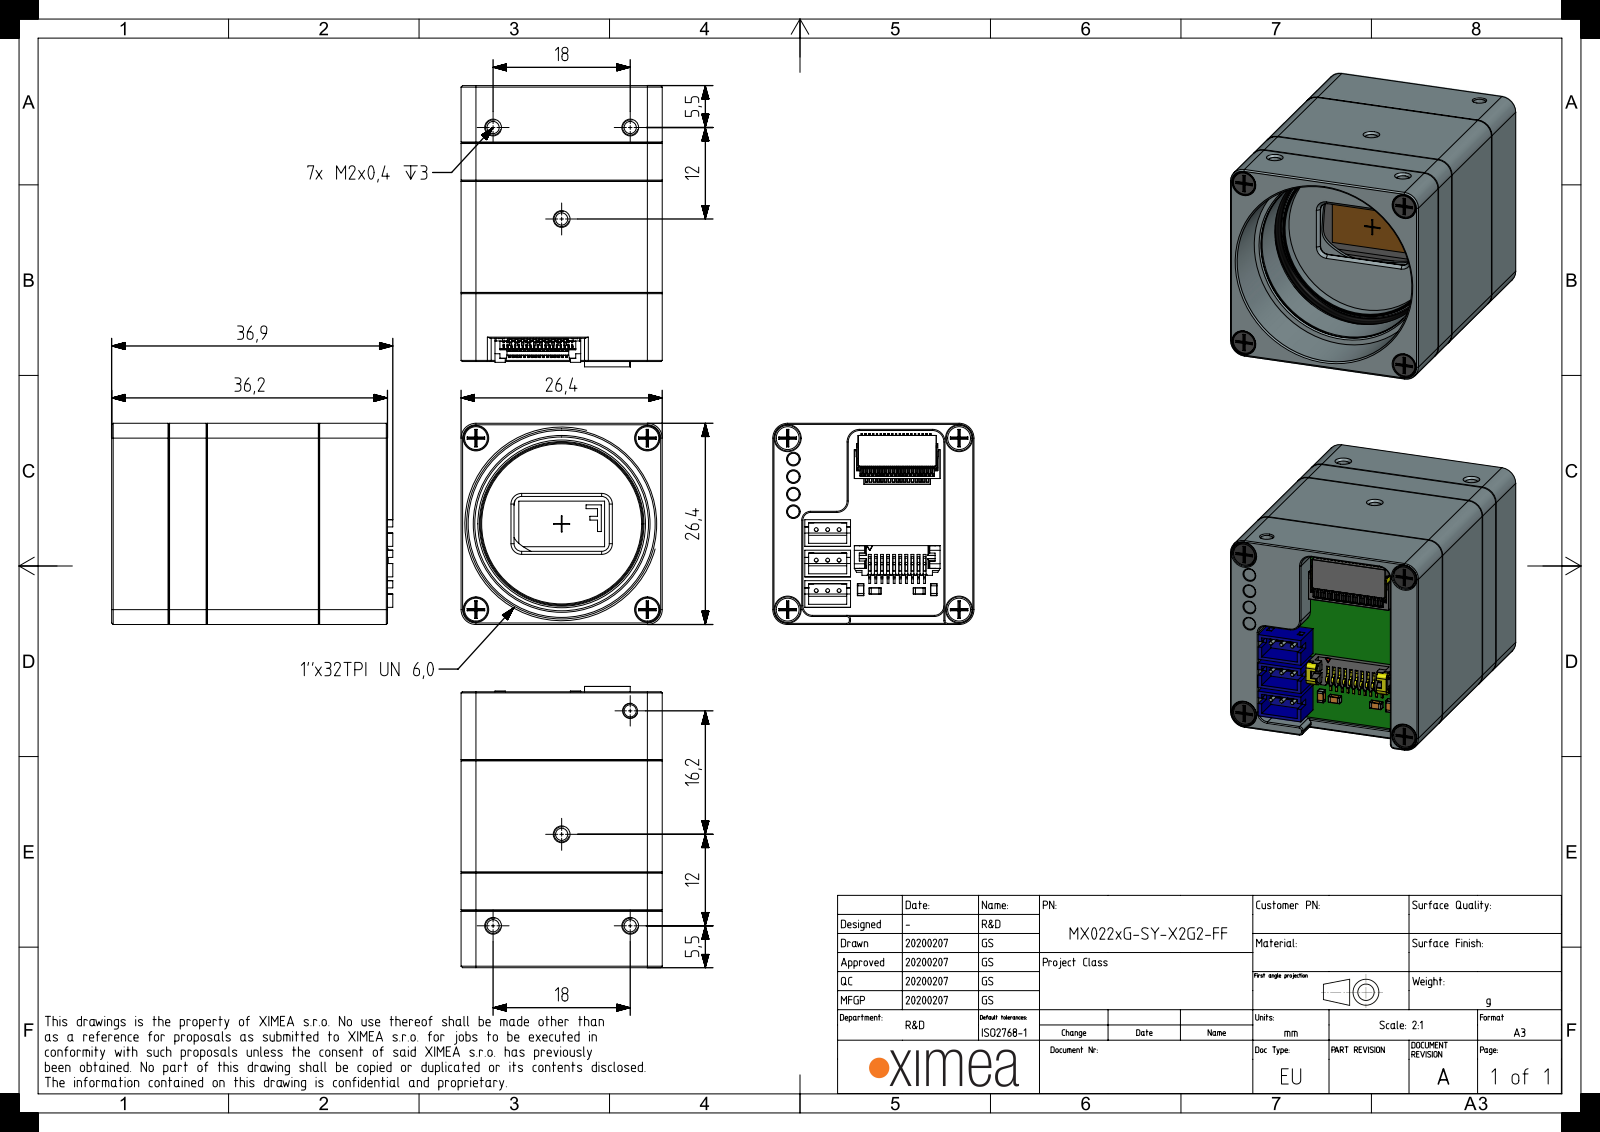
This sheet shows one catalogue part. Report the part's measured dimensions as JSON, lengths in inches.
{"part_name": "CMV2000_Glass; CMV2000_Package; MX-X2G2-MAIN-FF-PCA-REV2; MECH-THERM-PAD-10X5X1 (+8 more)", "step_written_by": "SIEMENS PLM Software NX 1907 (AUTOMOTIVE_DESIGN)", "units": "inches", "bodies": {"solids": 157, "faces": 11195, "planar": 7479, "cylindrical": 3279, "other": 437}, "overall_size": [1.453, 1.039, 1.039], "volume_in3": 0.696, "surface_area_in2": 34.27, "round_holes": [[0.03, 95], [0.063, 16], [0.028, 9], [0.079, 8], [0.02, 5], [0.035, 4], [0.035, 4], [0.071, 4], [0.083, 4], [0.118, 4], [0.126, 4], [0.132, 4]], "round_bosses_or_shafts": [[0.012, 95], [0.02, 9], [0.075, 8], [0.118, 6], [0.064, 4], [0.033, 4], [0.063, 2], [0.031, 2]], "partial_cylinders_radius": [[0.004, 61], [0.013, 28], [0.015, 27], [0.006, 24], [0.039, 24], [0.059, 22], [0.051, 16], [0.012, 15]], "face_to_face_distances": [1.039, 0.039, 0.142, 0.224, 0.305, 0.622, 0.102, 0.185, 0.583, 0.366], "hole_center_spacings": [0.05, 0.071, 0.112, 0.1, 0.158, 0.15, 0.206, 0.2]}
